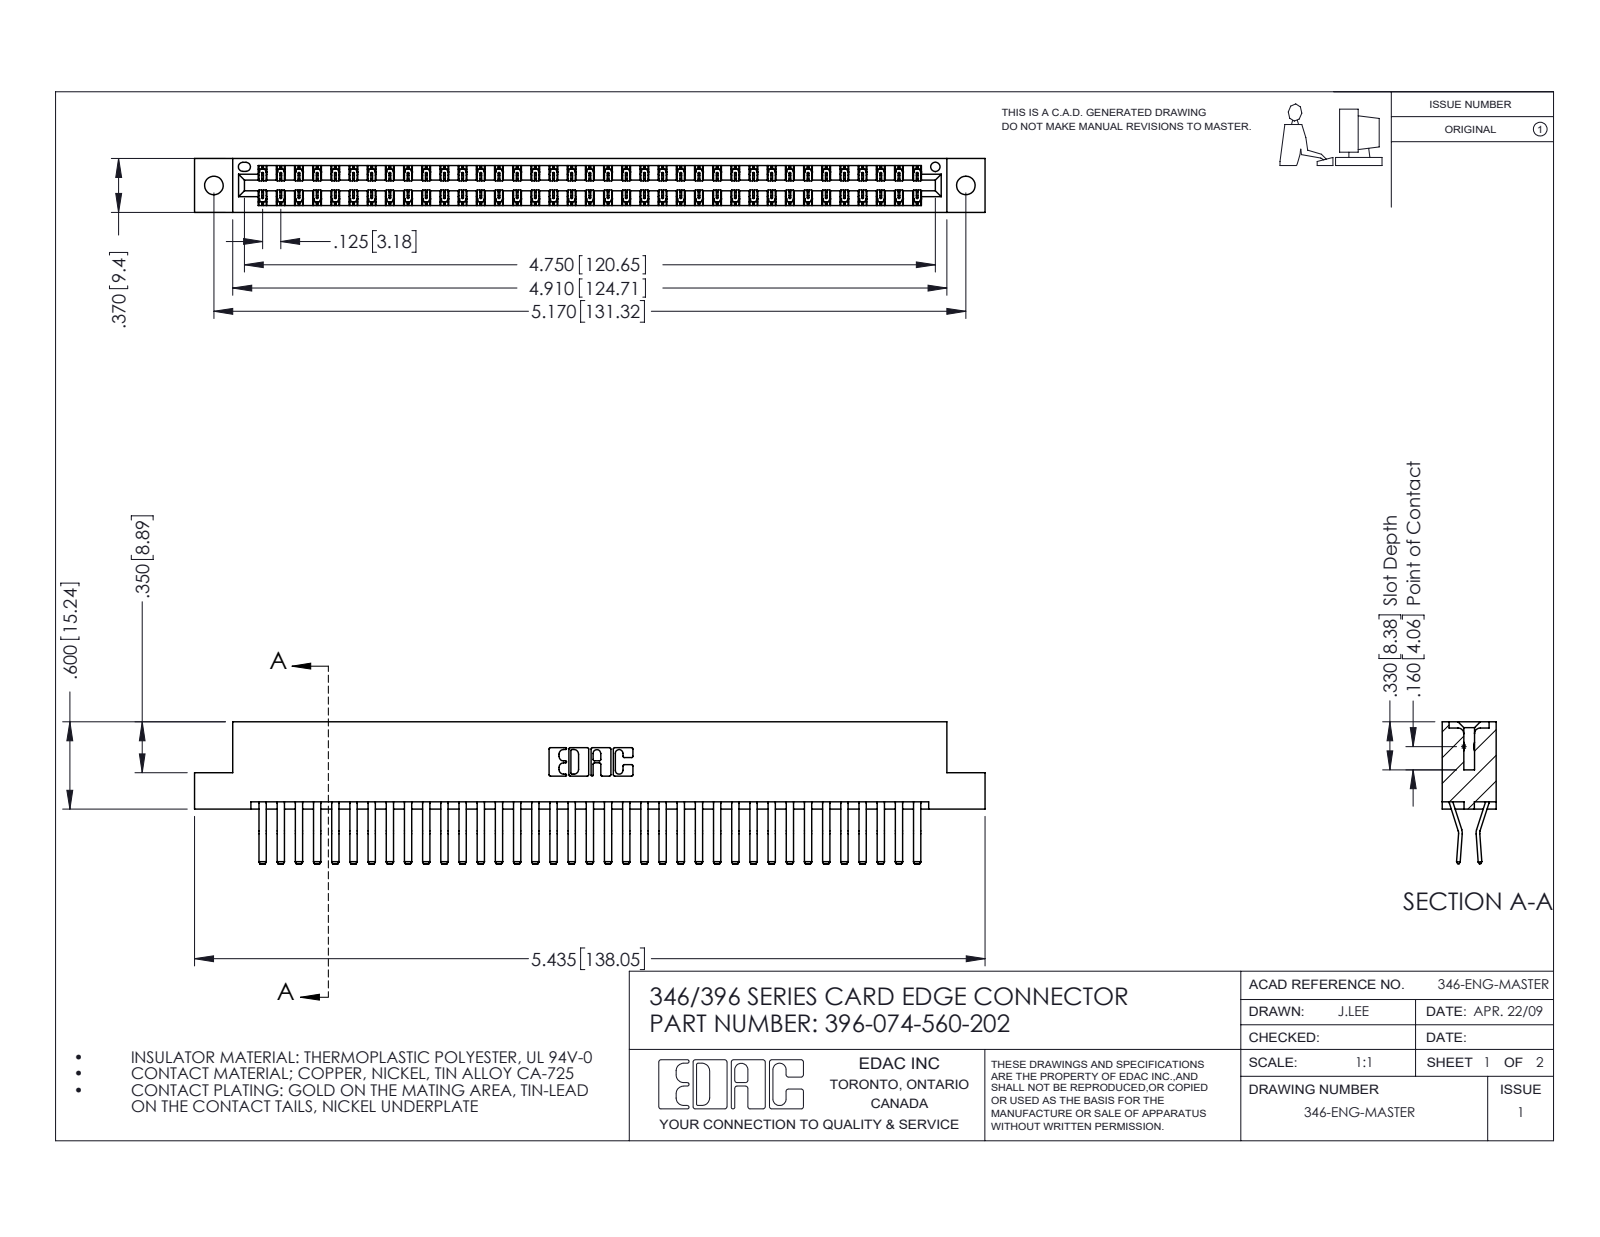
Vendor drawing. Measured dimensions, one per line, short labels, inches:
name: 396-074-560-202; 345-292-001_560 Tail; 346 Part_Flush Mounting Lugs - 0.128 Dia
written by: SolidWorks 2016 (CONFIG_CONTROL_DESIGN)
unit: in
bodies: 75 solids, 4118 faces (2666 planar, 1452 cylindrical, 0 other)
size: 5.435 × 0.975 × 0.37
volume: 0.846 in³; area: 31.02 in²
holes: 2× ⌀0.128, 1× ⌀0.064
rounds: 111× R0.006, 22× R0.01, 6× R0.007, 6× R0.031, 3× R0.026, 2× R0.01, 2× R0.014, 2× R0.022
face distances: 0.048, 0.322, 0.37, 0.025, 0.25, 0.072, 0.298, 0.275, 0.148, 0.222
hole spacings: 0.246, 4.961, 5.17
